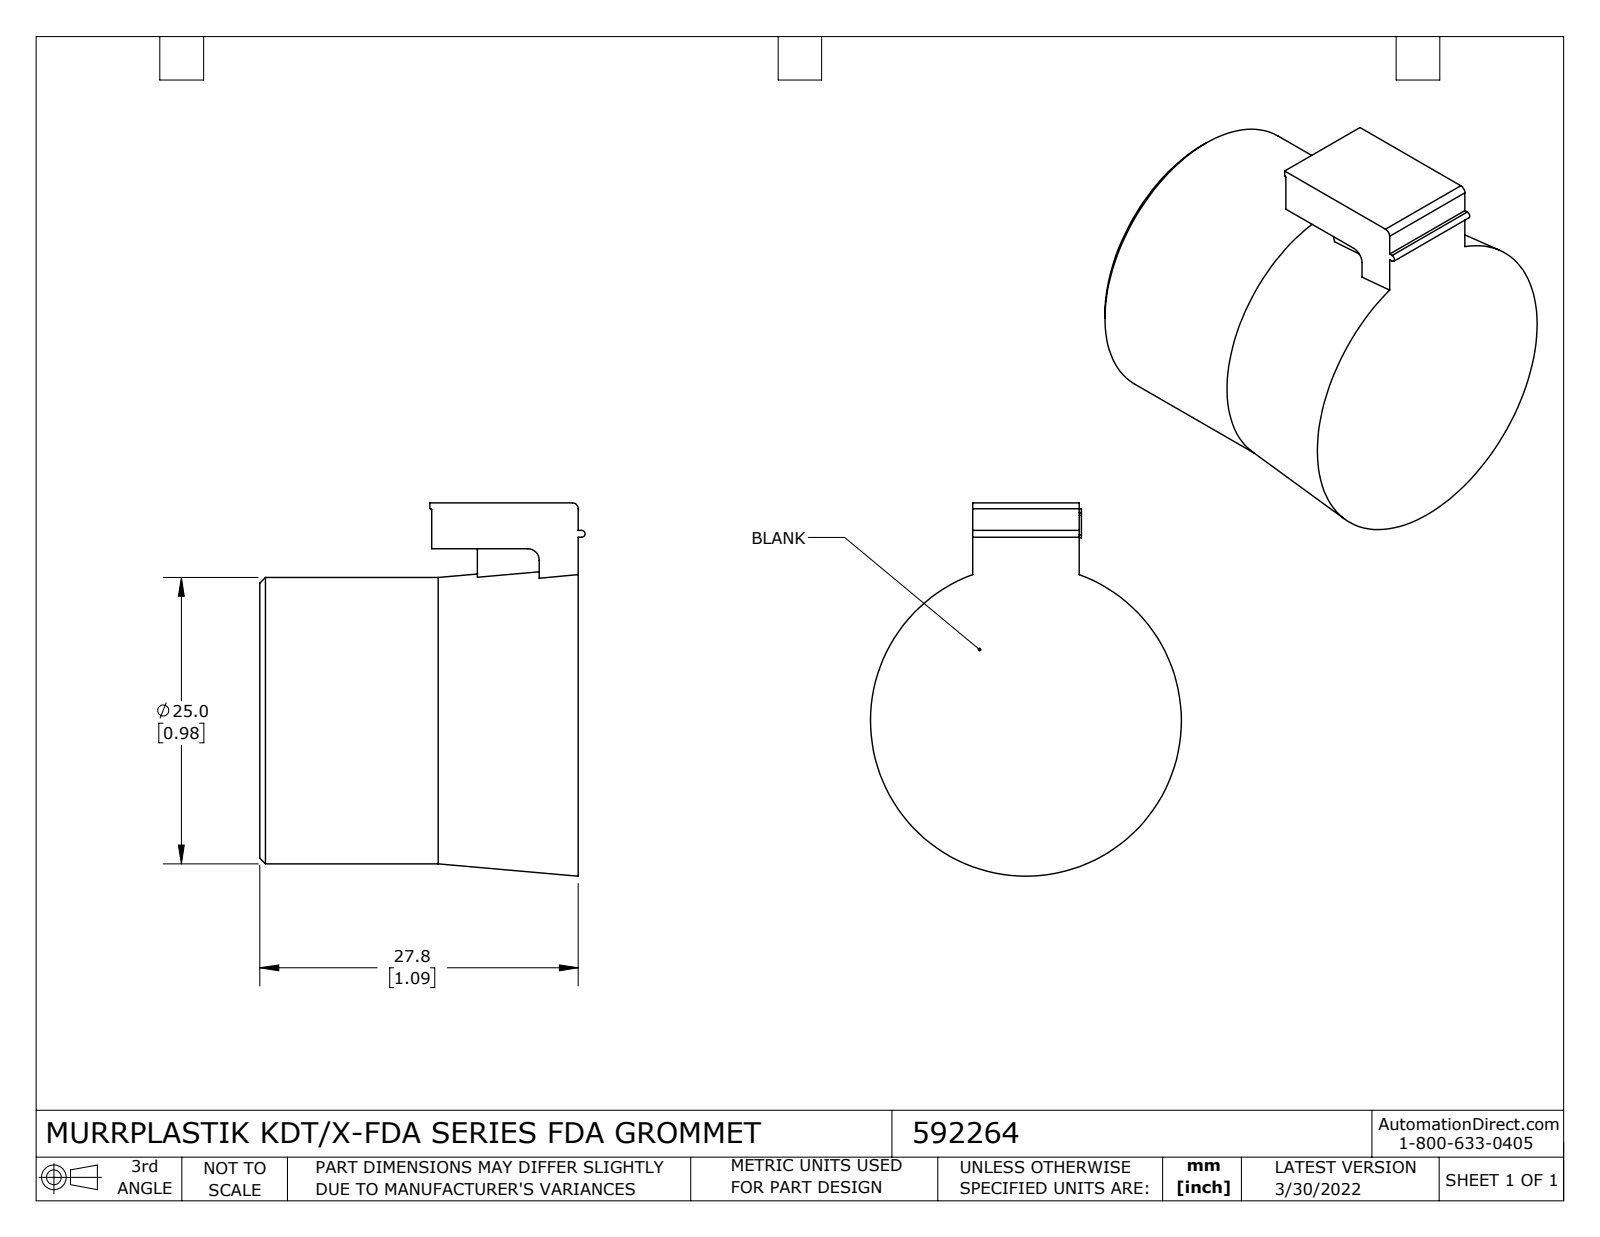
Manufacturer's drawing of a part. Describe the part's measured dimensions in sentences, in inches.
The part is named "592264". Its 3-D file was written by "SolidWorks 2021 (CONFIG_CONTROL_DESIGN)". It is 1 solid with 44 faces: 28 planar, 9 cylindrical and 7 other. Overall it measures 1.282 by 1.118 by 1.069 inches. Its volume is 0.601 cubic inches and its surface area 7.373 square inches. Round holes: 1 of diameter 0.669. Round bosses or shafts: 1 of diameter 0.984. Partial cylindrical surfaces (rounded edges, fillets, slot ends): 1 of radius 0.004, 1 of radius 0.012, 1 of radius 0.02, 1 of radius 0.039. The main face-to-face distances are 1.094, 0.157, 0.366, 0.504, 0.591, 0.346, 0.748, 0.134, 0.213, 0.37.
